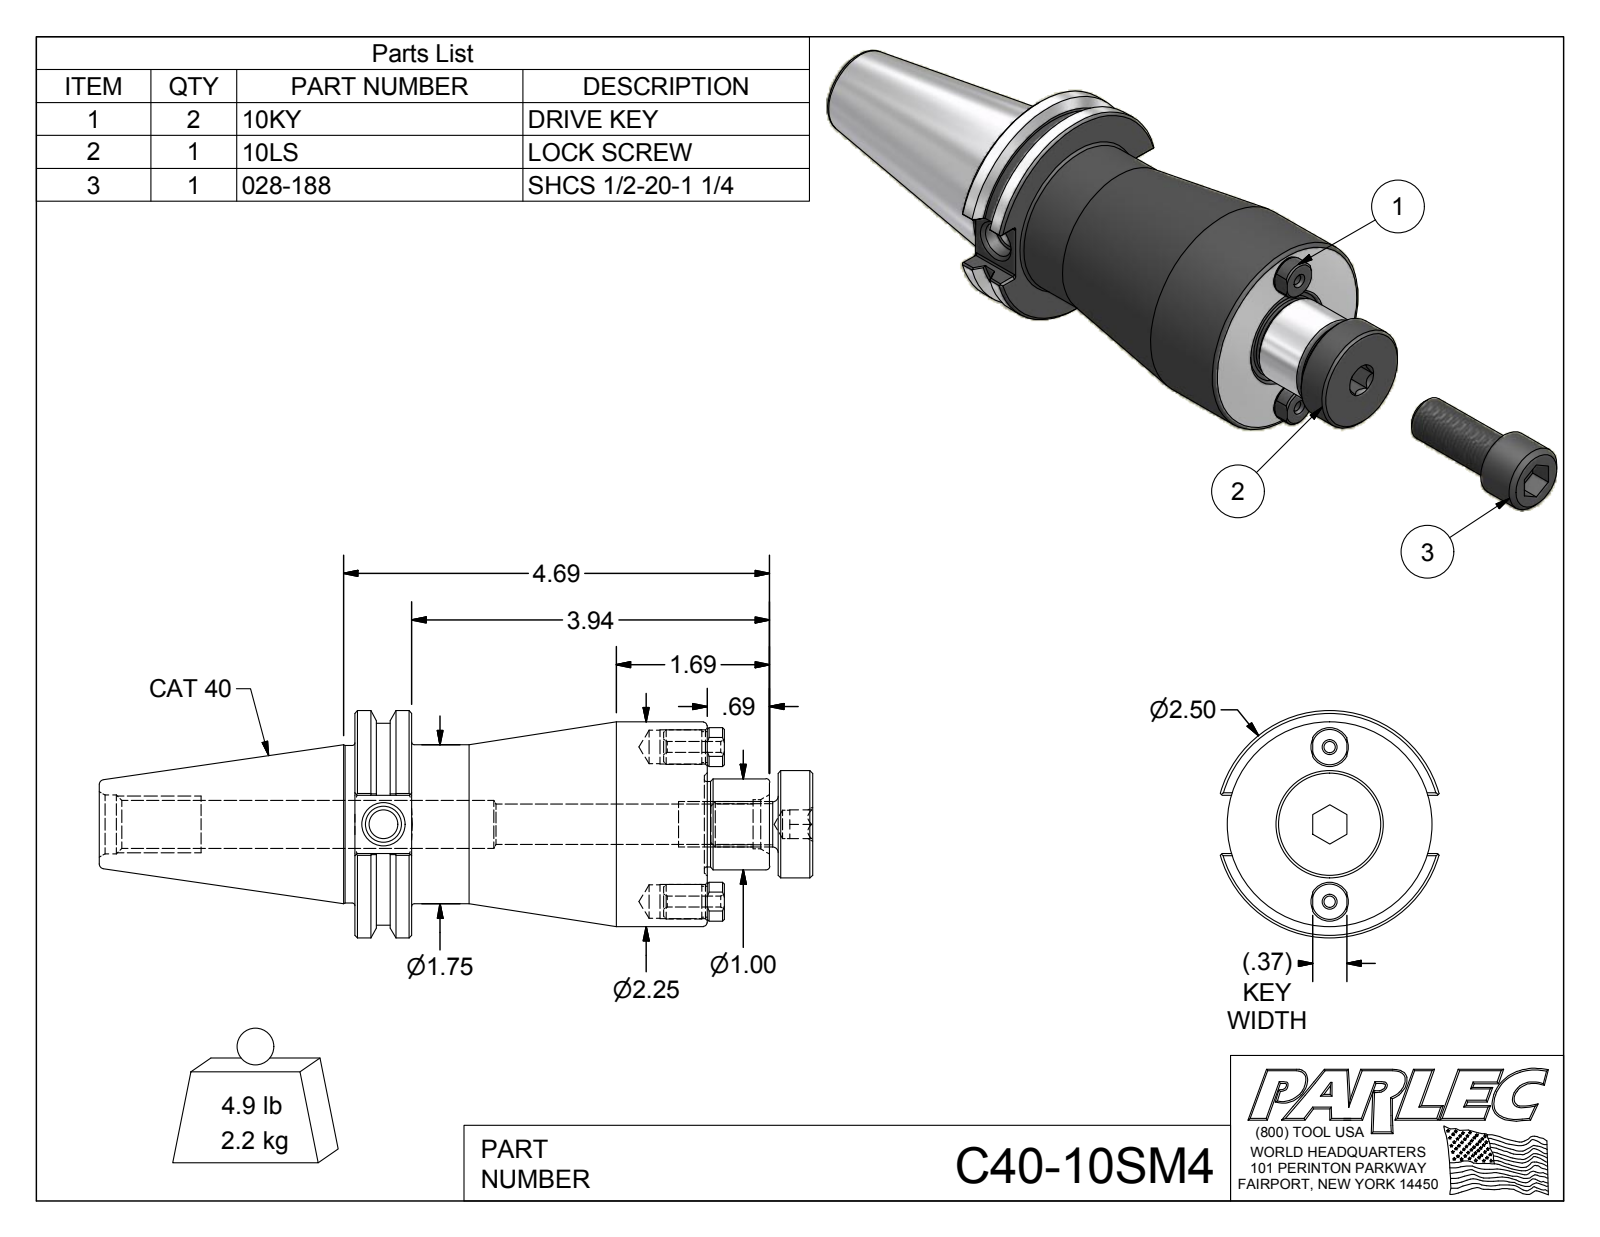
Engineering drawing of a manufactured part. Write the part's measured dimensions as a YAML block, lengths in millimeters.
part_name: "C40-10SM4; C40-10SM4-1; 028-188; 10KY (+1 more)"
step_written_by: "Autodesk Inventor 2012 (AUTOMOTIVE_DESIGN)"
units: millimeters
bodies: {solids: 5, faces: 175, planar: 68, cylindrical: 48, other: 59}
overall_size: [268.4, 63.5, 61.1]
volume: 286900
surface_area: 48290
round_holes:
  - {diameter: 3, count: 2}
  - {diameter: 9.3, count: 2}
  - {diameter: 9.5, count: 2}
  - {diameter: 7.9, count: 1}
  - {diameter: 8, count: 1}
  - {diameter: 10.1, count: 1}
  - {diameter: 11.3, count: 1}
  - {diameter: 13.4, count: 1}
  - {diameter: 13.7, count: 1}
  - {diameter: 16.5, count: 1}
round_bosses_or_shafts:
  - {diameter: 9.7, count: 2}
  - {diameter: 8.6, count: 2}
  - {diameter: 63.5, count: 1}
  - {diameter: 57.2, count: 1}
  - {diameter: 56.4, count: 1}
  - {diameter: 44.5, count: 1}
  - {diameter: 43.9, count: 1}
  - {diameter: 30, count: 1}
partial_cylinders:
  - {radius: 0.5, count: 12}
  - {radius: 5.4, count: 2}
face_to_face_distances: [98.4, 15.9, 82.6, 127.9, 112, 29.4, 118.2, 102.3, 19.8, 9.7]
hole_center_spacings: [21.6, 43.2]
